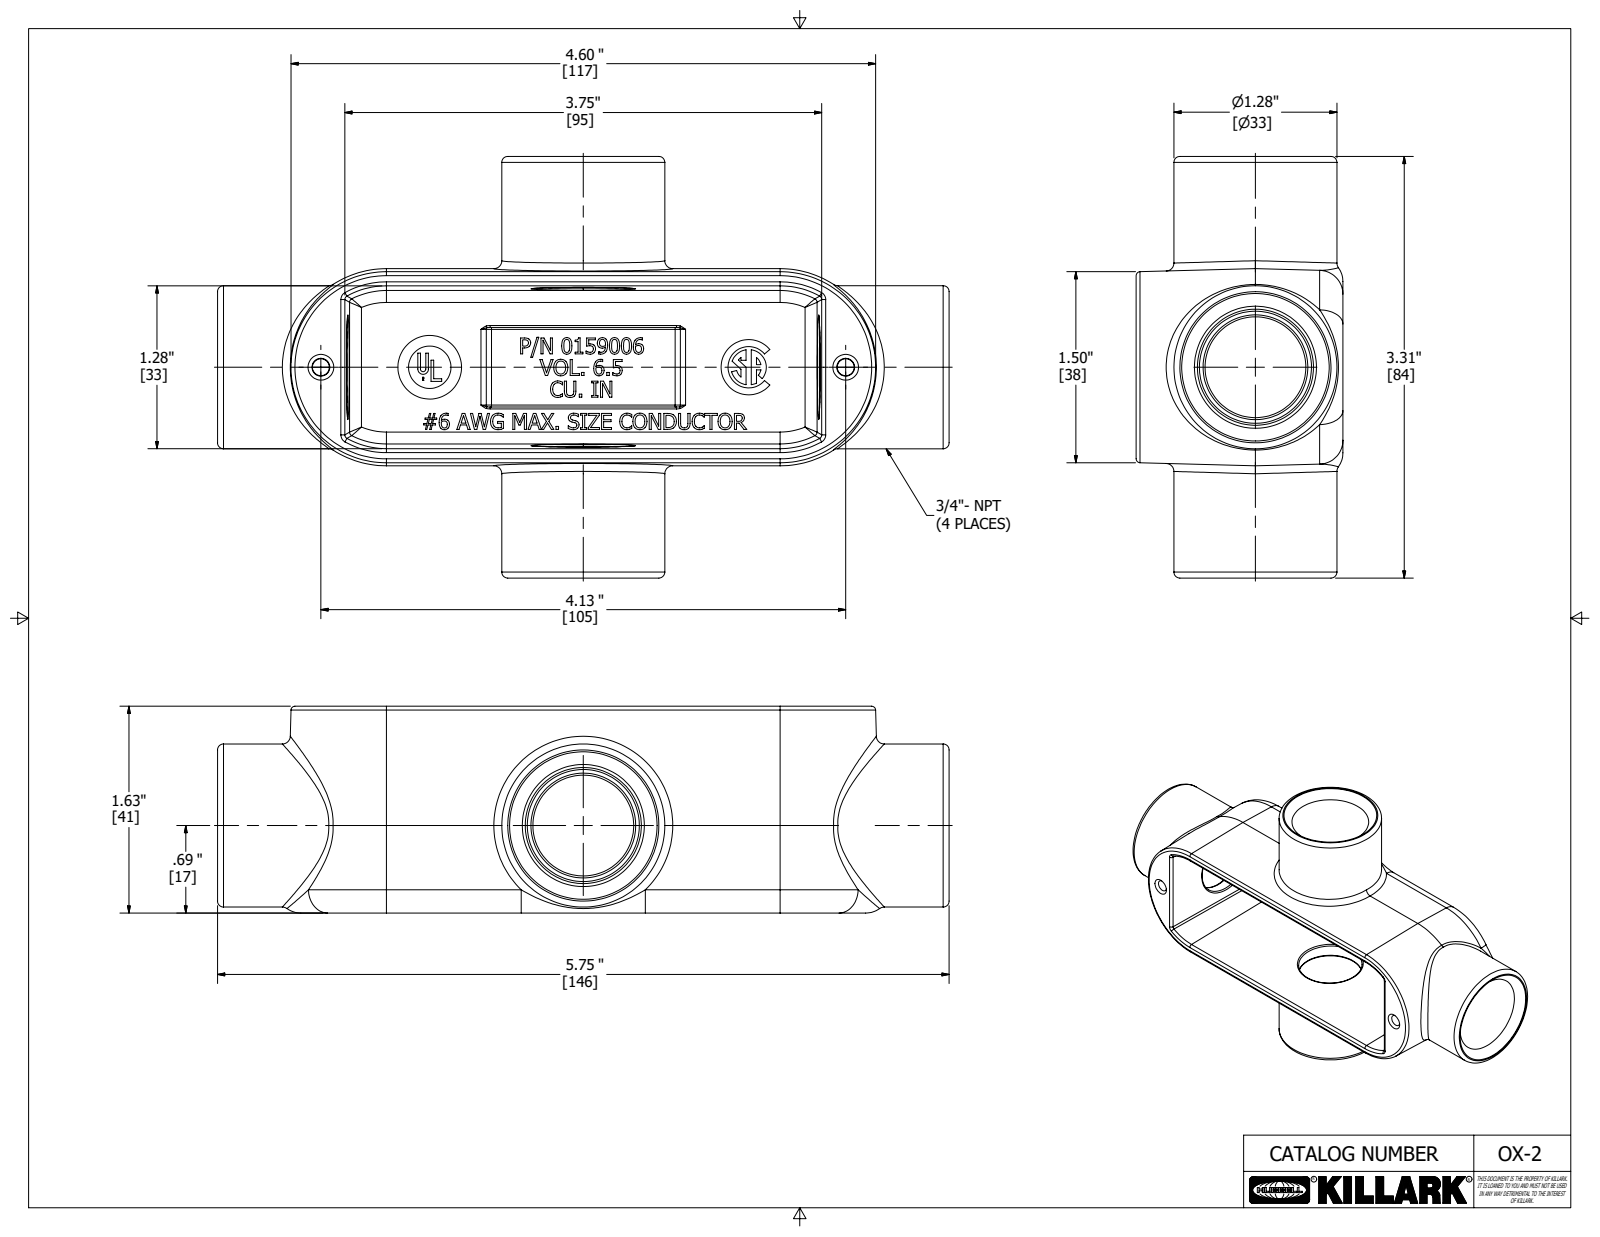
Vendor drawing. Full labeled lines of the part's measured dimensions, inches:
Part name (STEP PRODUCT): 11911-1
STEP written by: Autodesk Inventor 2018 (AUTOMOTIVE_DESIGN)
Units: inches
Bodies: 1 solid, 1036 faces (554 planar, 52 cylindrical, 430 other)
Overall size (bounding box): 5.75 × 3.313 × 1.639
Volume: 4.742 in³ · Surface area: 63.63 in²
Round holes (diameter × count): ⌀0.792 ×2, ⌀0.333 ×1
Round bosses / shafts (diameter × count): ⌀1.281 ×2, ⌀0.5 ×1
Partial cylindrical surfaces — rounded edges, fillets, slot ends (radius × count): R0.031 ×14, R0.015 ×4, R0.062 ×4, R0.094 ×4, R0.187 ×2, R0.021 ×1, R0.042 ×1, R0.098 ×1
Main face-to-face distances: 1.391, 0.094, 1.549, 0.158, 0.031, 1.625, 1.531, 0.125, 0.063, 1.594
